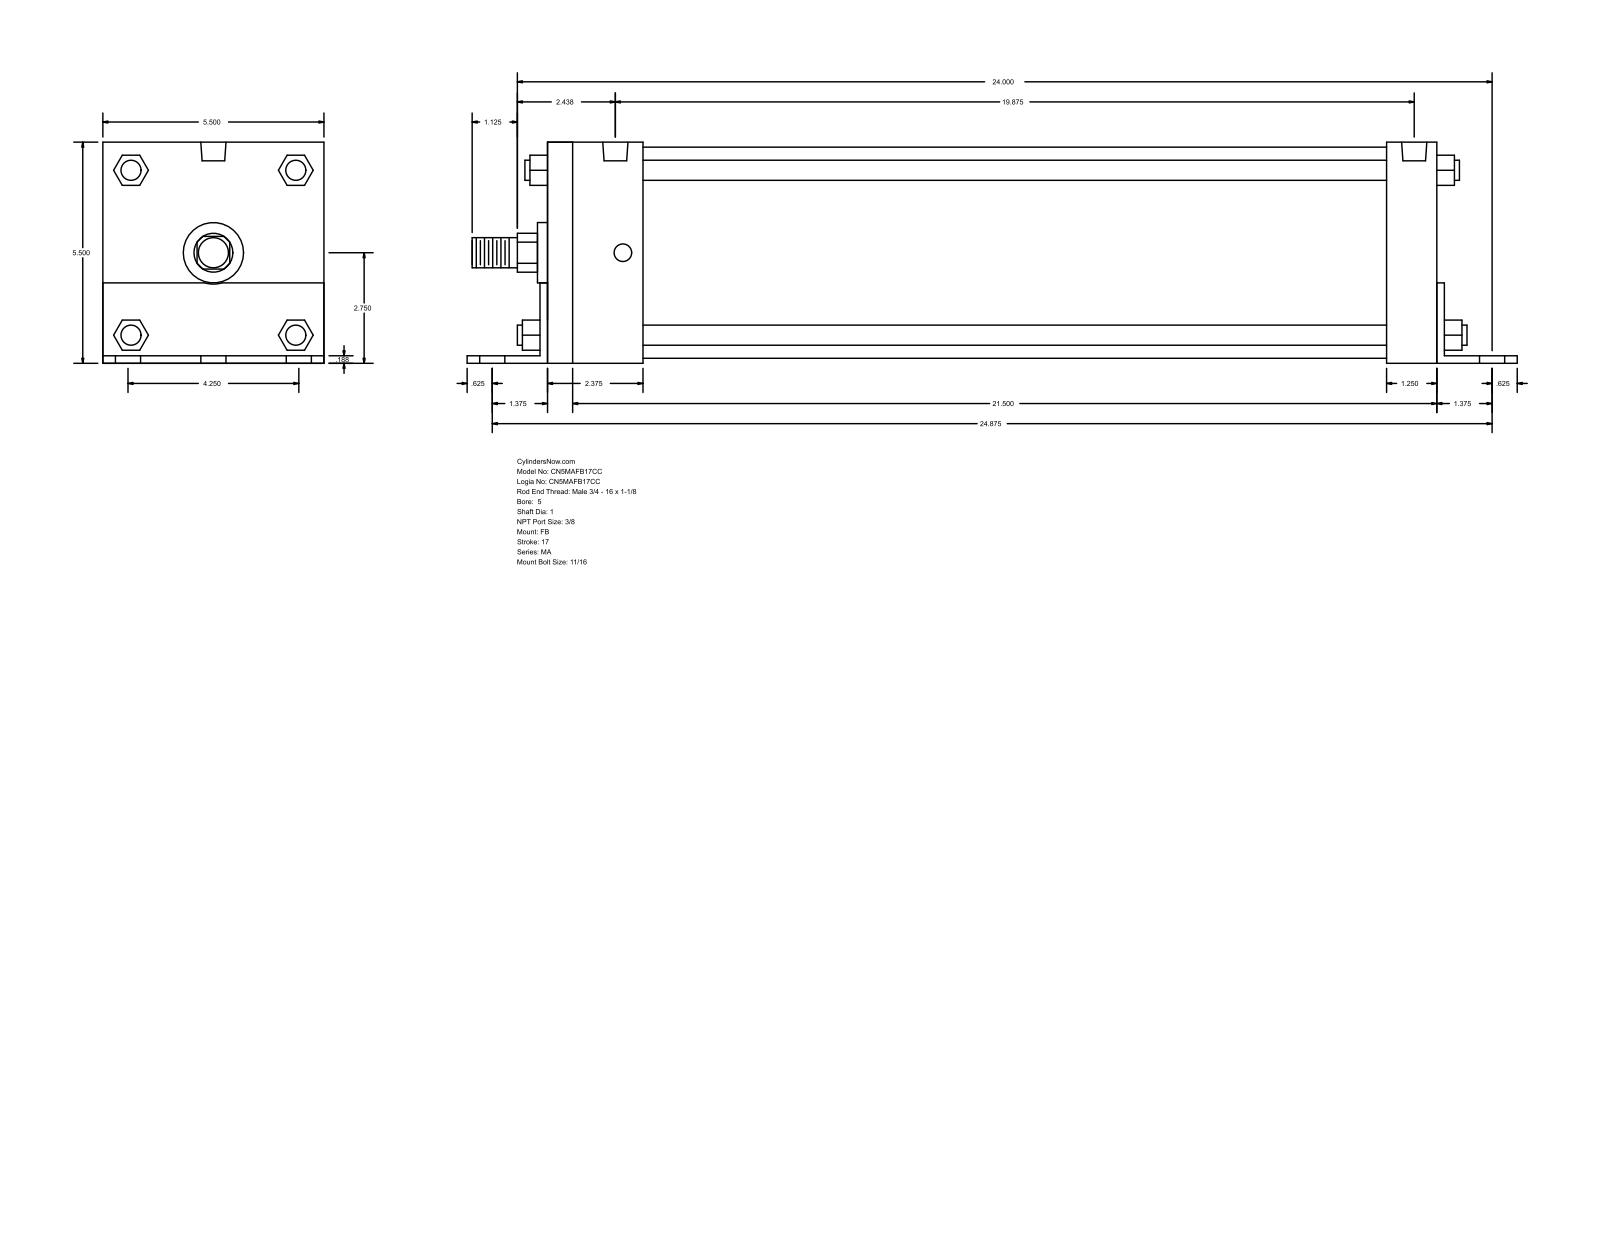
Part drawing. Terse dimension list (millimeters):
name: MA_FB__0500_1
written by: GSSL Pune (CONFIG_CONTROL_DESIGN)
unit: mm
bodies: 0 solids, 140 faces (105 planar, 35 cylindrical, 0 other)
size: 663.58 × 139.75 × 139.7
holes: 6× ⌀17.46, 4× ⌀11.11, 2× ⌀15.93
bosses: 4× ⌀12.7, 1× ⌀133.35, 1× ⌀38.1, 1× ⌀25.4, 1× ⌀19.05
rounds: 1× R12.29, 1× R19.81
face distances: 139.7, 4.76, 139.75, 4.71, 134.99, 561.97, 4.77, 566.74, 566.73, 571.5
hole spacings: 53.98, 634.13, 631.83, 4.76, 73.04, 76.33, 94.68, 98.63
